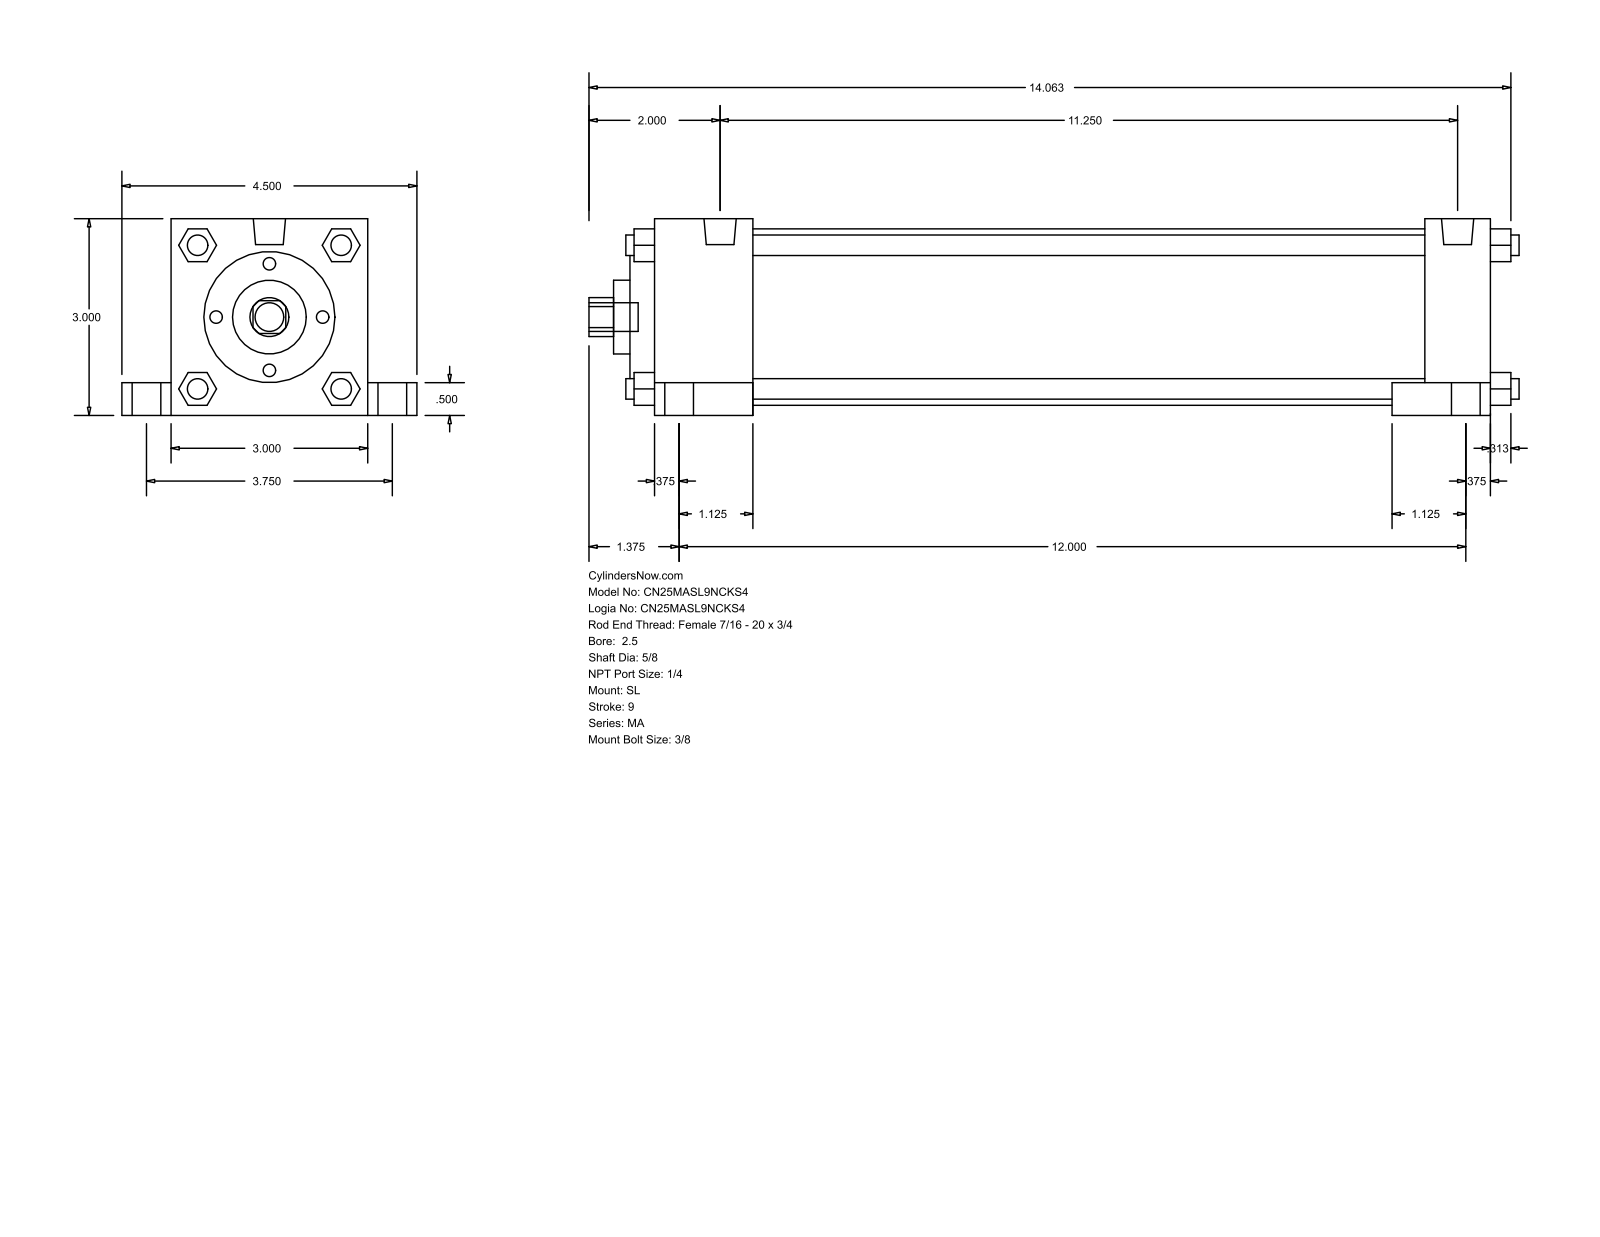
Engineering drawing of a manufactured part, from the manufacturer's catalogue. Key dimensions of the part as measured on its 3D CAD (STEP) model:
Part name (STEP PRODUCT): MA_SL__0250_0.625
STEP written by: GSSL Pune (CONFIG_CONTROL_DESIGN)
Units: millimetres
Bodies: 0 solids, 150 faces (113 planar, 37 cylindrical, 0 other)
Overall size (bounding box): 360.36 × 114.3 × 76.2
Round holes (diameter × count): ⌀15.88 ×1, ⌀28.57 ×1, ⌀50.8 ×1, ⌀68.33 ×1
Round bosses / shafts (diameter × count): ⌀7.94 ×8, ⌀11.11 ×5, ⌀17.46 ×4, ⌀12.49 ×2
Partial cylindrical surfaces — rounded edges, fillets, slot ends (radius × count): R7.54 ×1
Main face-to-face distances: 76.2, 323.85, 12.7, 260.35, 25.4, 38.1, 285.75, 298.45, 19.05, 63.5
